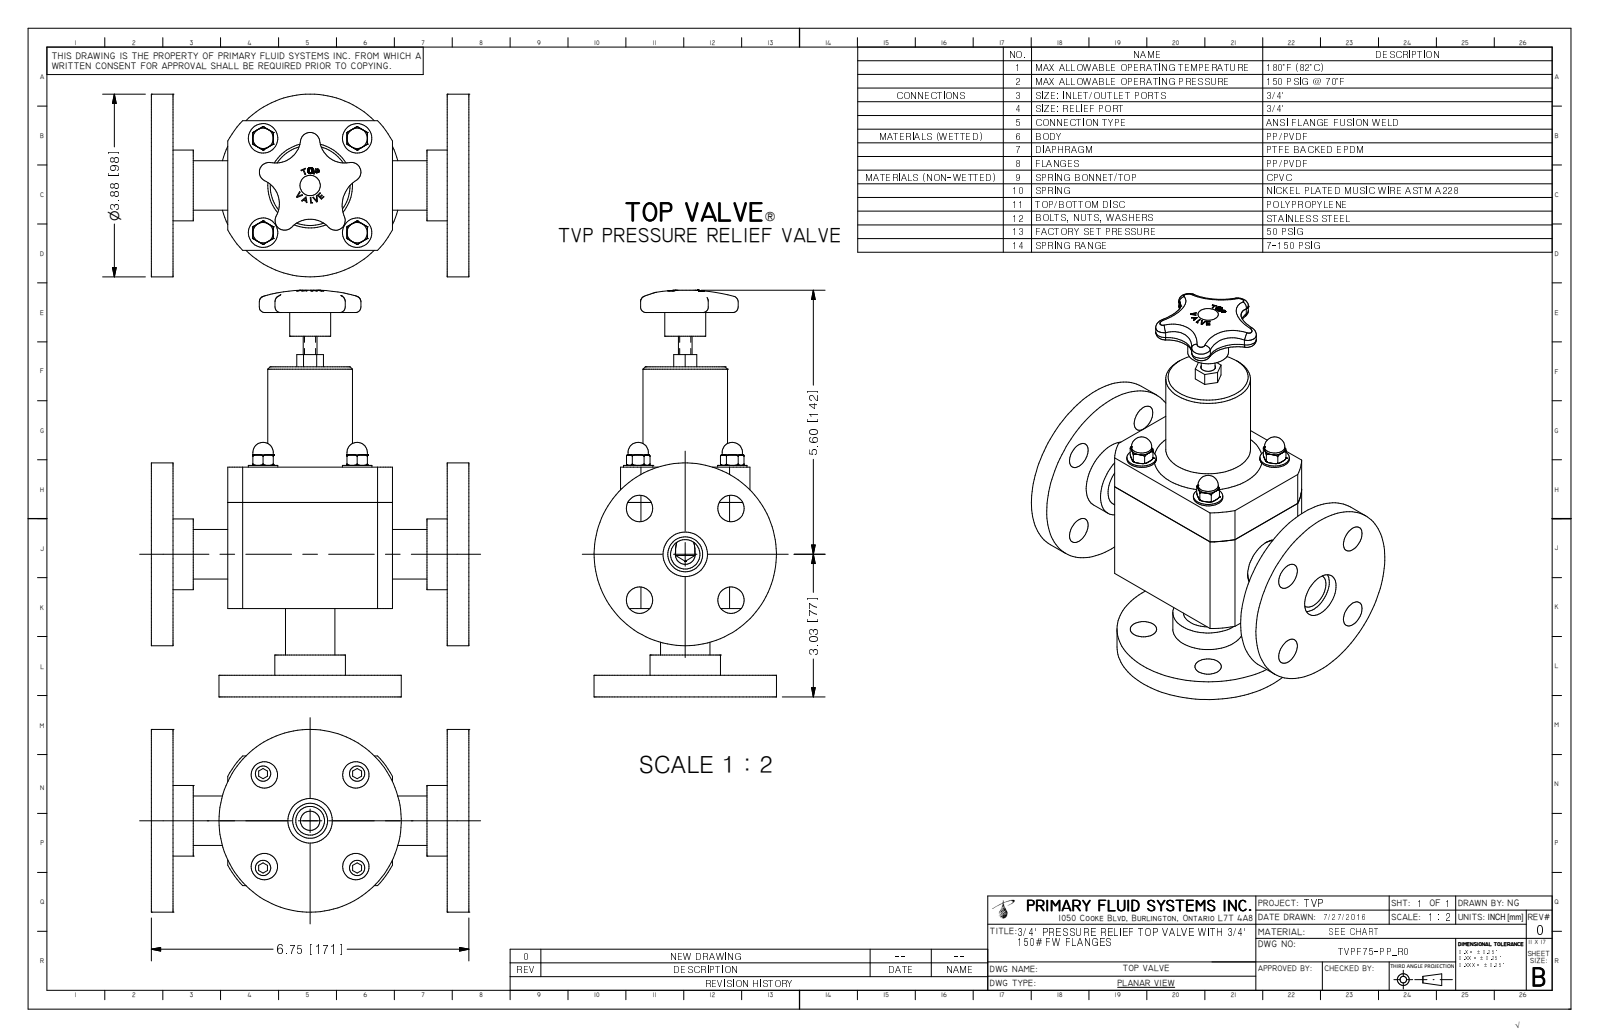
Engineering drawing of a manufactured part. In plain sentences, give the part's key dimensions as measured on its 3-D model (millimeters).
The part is named "TVPF75-PP_R0". Its 3-D file was written by "Autodesk Inventor 2009 (AUTOMOTIVE_DESIGN)". It is 1 solid with 340 faces: 135 planar, 68 cylindrical and 137 other. Overall it measures 219.1 by 171.5 by 98.4 millimeters. Its volume is 847 700 cubic millimeters and its surface area 125 800 square millimeters. Round holes: 8 of diameter 14.2, 4 of diameter 4.4, 2 of diameter 18.8, 2 of diameter 24, 1 of diameter 61. Round bosses or shafts: 4 of diameter 15.9, 4 of diameter 11, 2 of diameter 98.4, 2 of diameter 38.1, 2 of diameter 26.7, 1 of diameter 60.3, 1 of diameter 45.7, 1 of diameter 22.1. Partial cylindrical surfaces (rounded edges, fillets, slot ends): 5 of radius 2.2, 5 of radius 5.2, 4 of radius 13.6, 4 of radius 16.7, 1 of radius 15.9, 1 of radius 18.9, 1 of radius 50.5. The main face-to-face distances are 11.7, 159.8, 130.2, 171.5, 41.3, 29.6, 118.5, 148.1, 69.9, 47.6. The hole center spacings are 34.9, 49.4, 50.1, 1, 35.9, 50.8, 69.9, 70.8.
